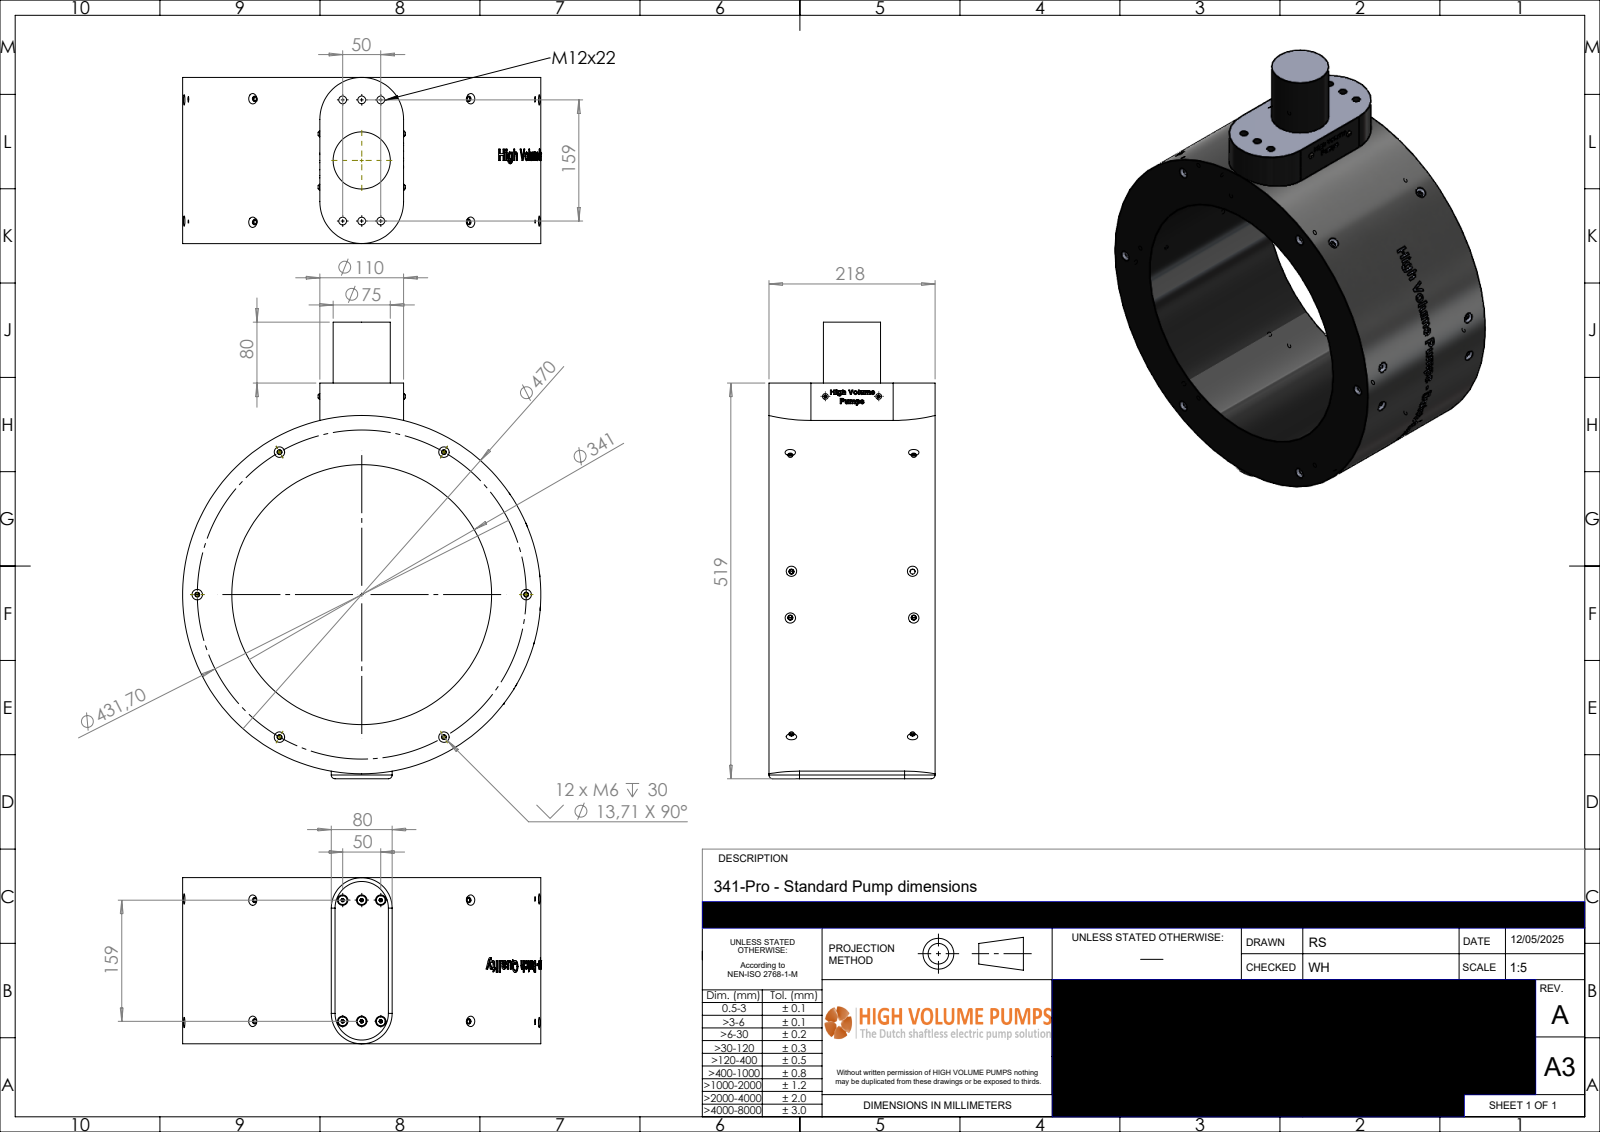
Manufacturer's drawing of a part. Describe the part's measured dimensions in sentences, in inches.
The part is named "P-341-530-rev-A-SP". Its 3-D file was written by "SolidWorks 2024 (AUTOMOTIVE_DESIGN)". It is 1 solid with 1204 faces: 551 planar, 138 cylindrical and 515 other. Overall it measures 23.584 by 18.504 by 8.583 inches. Its volume is 1 178 cubic inches and its surface area 1 224 square inches. Round holes: 22 of diameter 0.197, 22 of diameter 0.26, 6 of diameter 0.252, 6 of diameter 0.402, 1 of diameter 13.425. Round bosses or shafts: 6 of diameter 0.456, 6 of diameter 0.236, 2 of diameter 0.299, 1 of diameter 18.504, 1 of diameter 2.953. Partial cylindrical surfaces (rounded edges, fillets, slot ends): 2 of radius 0.197, 2 of radius 1.575, 2 of radius 2.165, 1 of radius 9.232. The main face-to-face distances are 8.583, 20.435, 3.15, 4.331, 23.584, 0.591, 3.74, 4.291, 0.02, 4.311. The hole center spacings are 6.319, 8.498, 6.26, 0.06, 0.061, 0.984, 6.337, 6.378.
